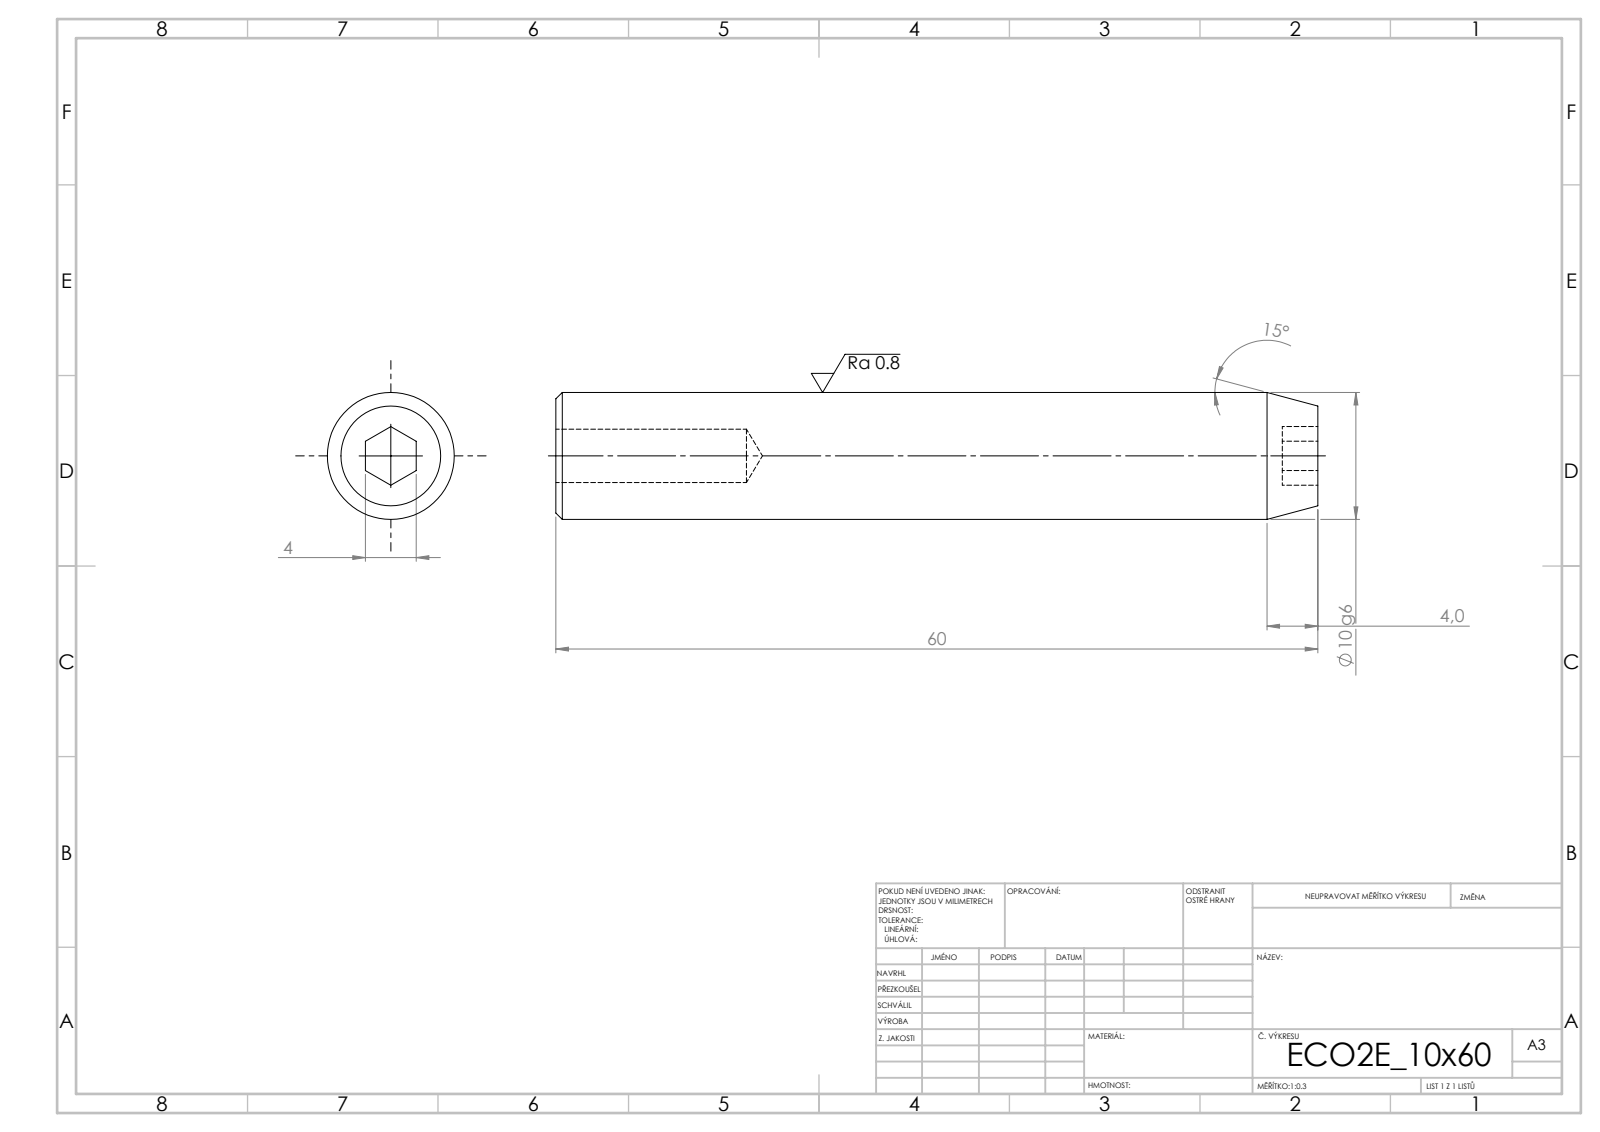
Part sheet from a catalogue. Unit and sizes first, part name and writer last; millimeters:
Units: millimetres
Overall size (bounding box): 60 × 10 × 10
Round holes (diameter × count): ⌀4.2 ×1
Round bosses / shafts (diameter × count): ⌀10 ×1
Main face-to-face distances: 60, 4, 2.8, 57.2
Volume: 4 394 mm³ · Surface area: 2 232 mm²
Bodies: 1 solid, 19 faces (9 planar, 4 cylindrical, 6 other)
STEP written by: SolidWorks 2019 (CONFIG_CONTROL_DESIGN)
